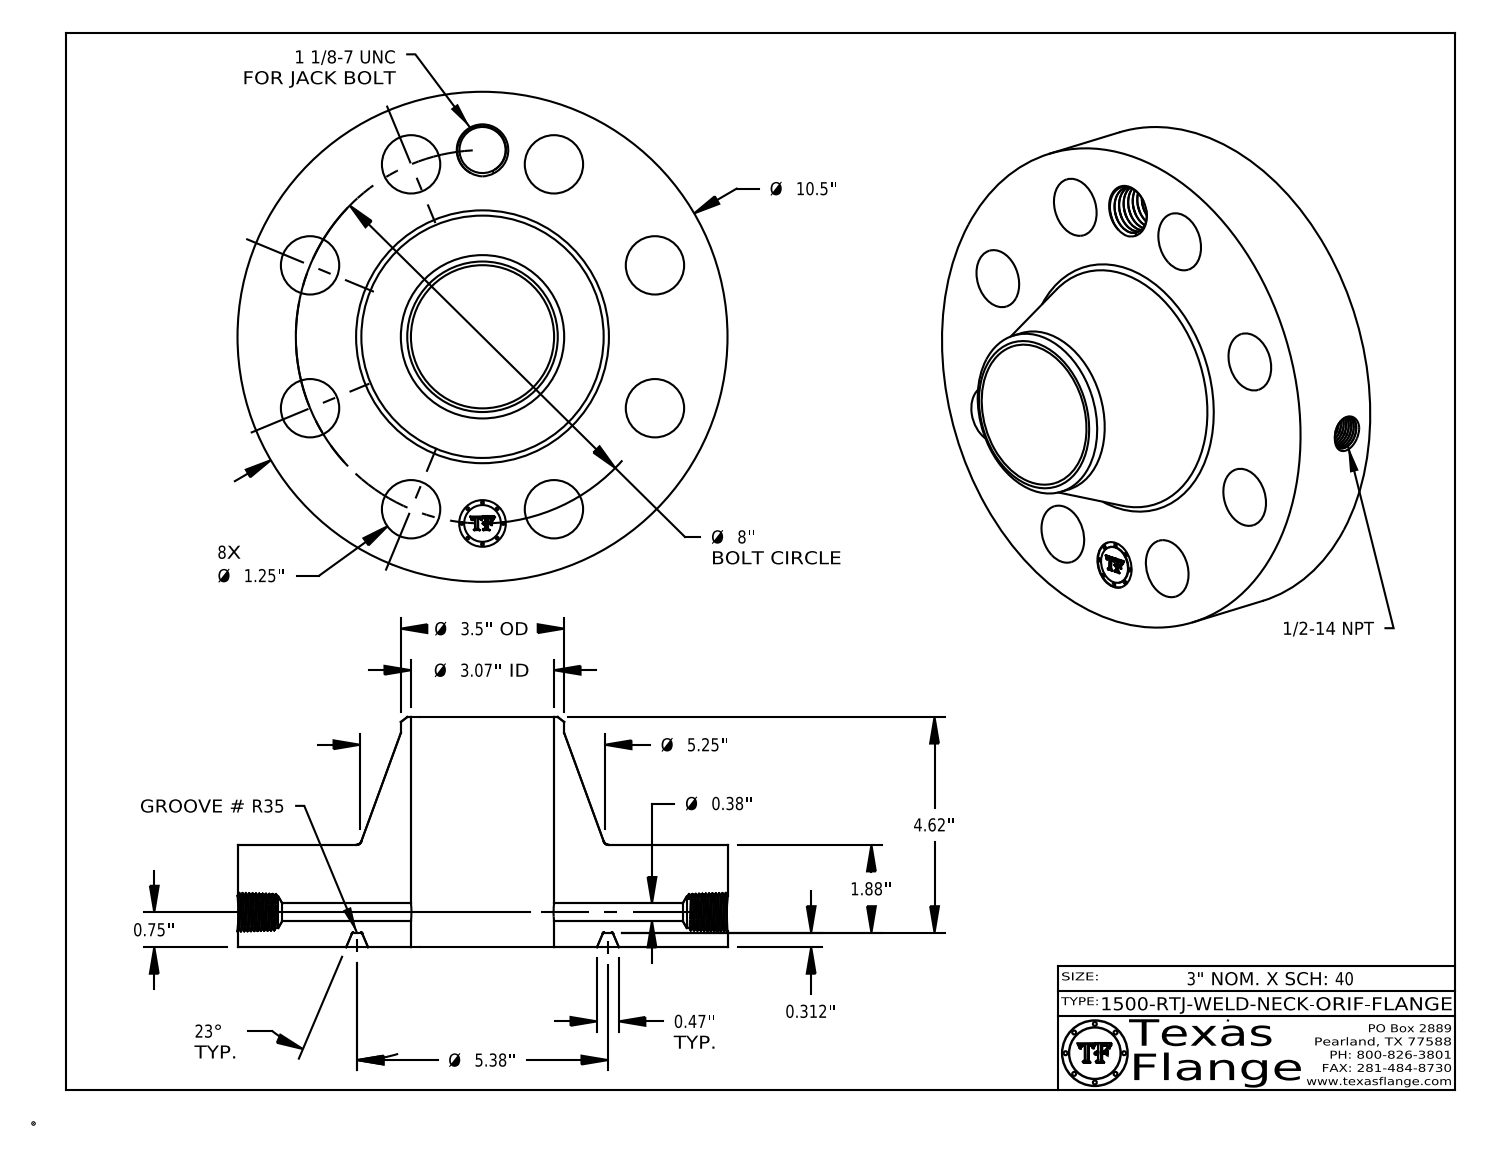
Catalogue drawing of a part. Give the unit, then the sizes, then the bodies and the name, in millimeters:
Units: millimetres
Overall size (bounding box): 266.7 × 266.7 × 125.3
Round holes (diameter × count): ⌀31.8 ×8, ⌀9.5 ×1, ⌀17.1 ×1, ⌀25 ×1, ⌀25.4 ×1, ⌀77.9 ×1
Round bosses / shafts (diameter × count): ⌀1.5 ×8, ⌀266.7 ×1, ⌀88.9 ×1, ⌀20 ×1
Main face-to-face distances: 55.7, 7.9, 47.8, 125.3, 117.3, 69.6, 55.3, 47.4, 0.4, 70
Hole centre spacings: 101.6, 143.7, 187.7, 39.6, 77.7, 77.8, 112.9, 169
Volume: 2 728 000 mm³ · Surface area: 246 200 mm²
Bodies: 1 solid, 779 faces (370 planar, 92 cylindrical, 317 other)
Part name (STEP PRODUCT): 1500-RTJ-WELD-NECK
STEP written by: CATIA V5 STEP AP214 (AUTOMOTIVE_DESIGN)
